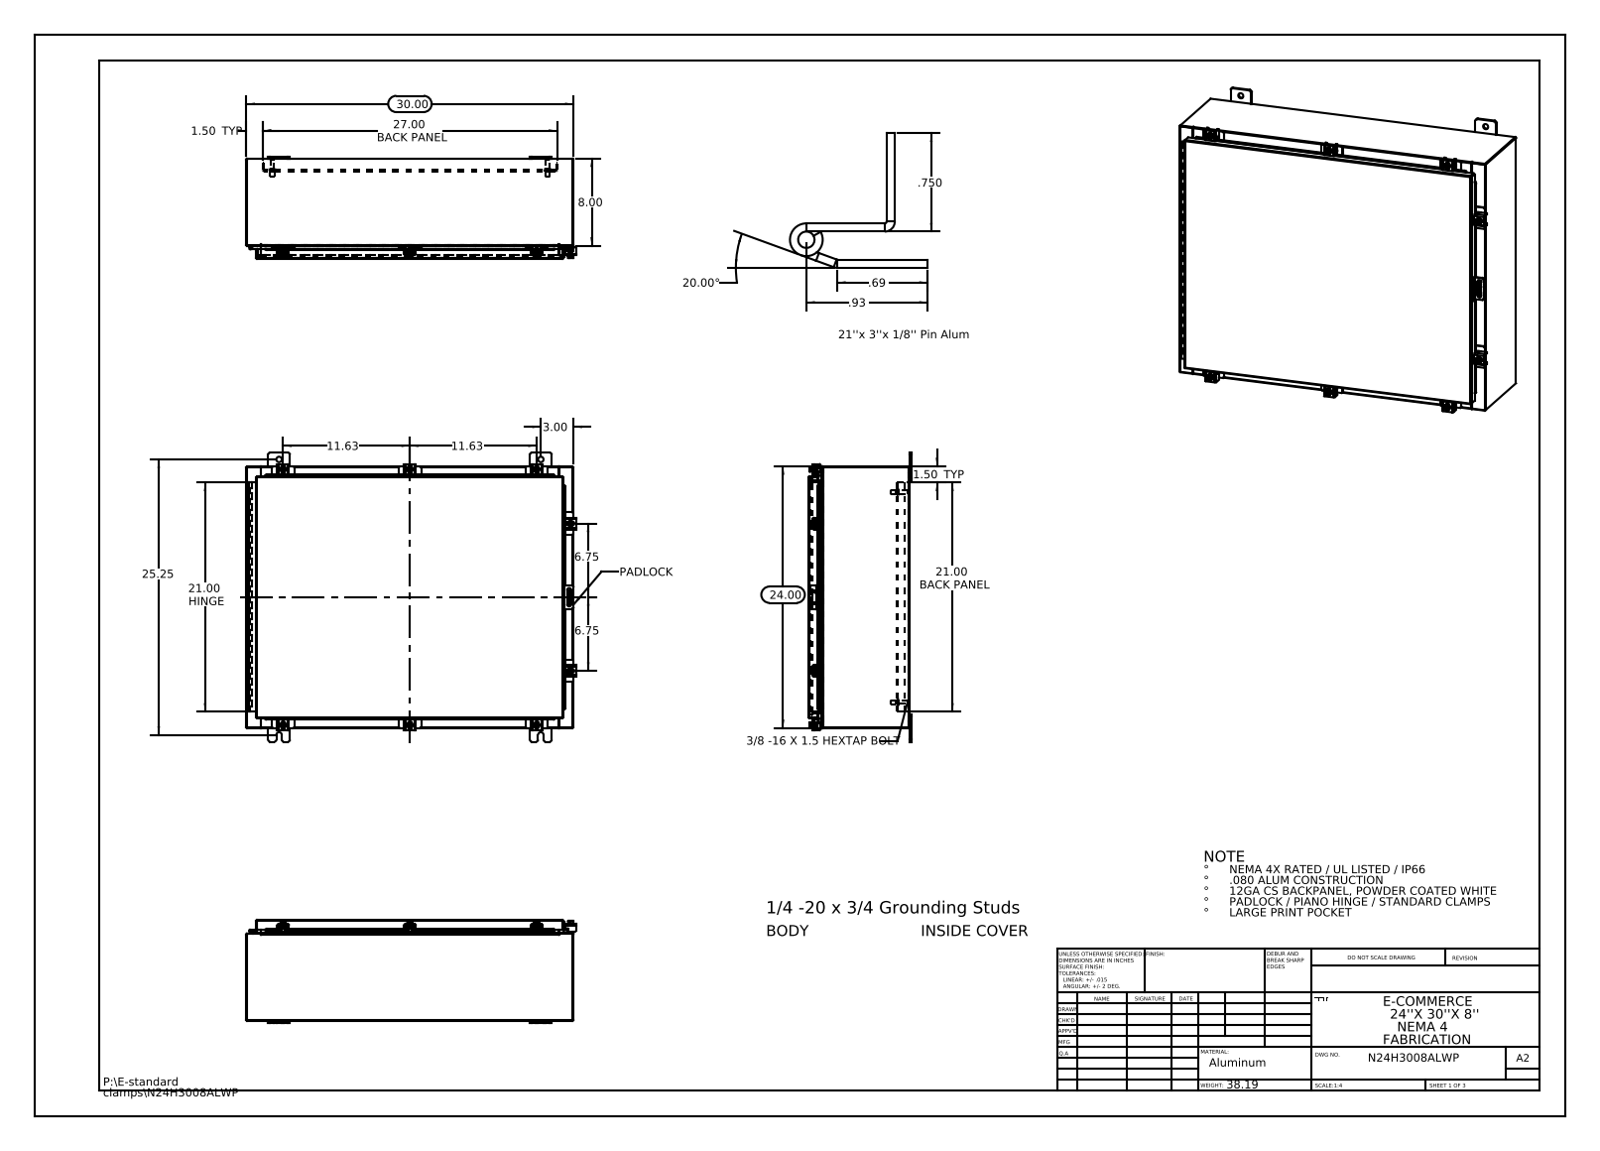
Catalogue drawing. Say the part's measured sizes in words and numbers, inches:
The part is named "N24H3008ALWP Hinge Enclosure Side2; N24H3008ALWP Clamp Top; N24H3008ALWP 125 Pin Hinge; N24H3008ALWP Body (+8 more)". Its 3-D file was written by "SolidWorks 2013 (CONFIG_CONTROL_DESIGN)". It is 57 solids with 1943 faces: 1028 planar, 803 cylindrical and 112 other. Overall it measures 30.211 by 26.5 by 9.389 inches. Its volume is 260.9 cubic inches and its surface area 6 534 square inches. Round holes: 8 of diameter 0.213, 8 of diameter 0.26, 8 of diameter 0.5, 2 of diameter 0.125, 1 of diameter 0.125. Round bosses or shafts: 9 of diameter 0.25, 8 of diameter 0.5, 8 of diameter 0.399, 4 of diameter 0.625, 4 of diameter 0.375, 4 of diameter 0.33. Partial cylindrical surfaces (rounded edges, fillets, slot ends): 38 of radius 0.06, 25 of radius 0.013, 24 of radius 0.19, 21 of radius 0.088, 16 of radius 0.12, 16 of radius 0.141, 11 of radius 0.05, 10 of radius 0.08. The main face-to-face distances are 0.075, 9.126, 9.201, 9.051, 0.104, 1, 1.075, 8.051, 8.126, 1.179. The hole center spacings are 21.374, 24, 26.174, 23.451, 1.858, 2.326, 2.326, 3.065.
